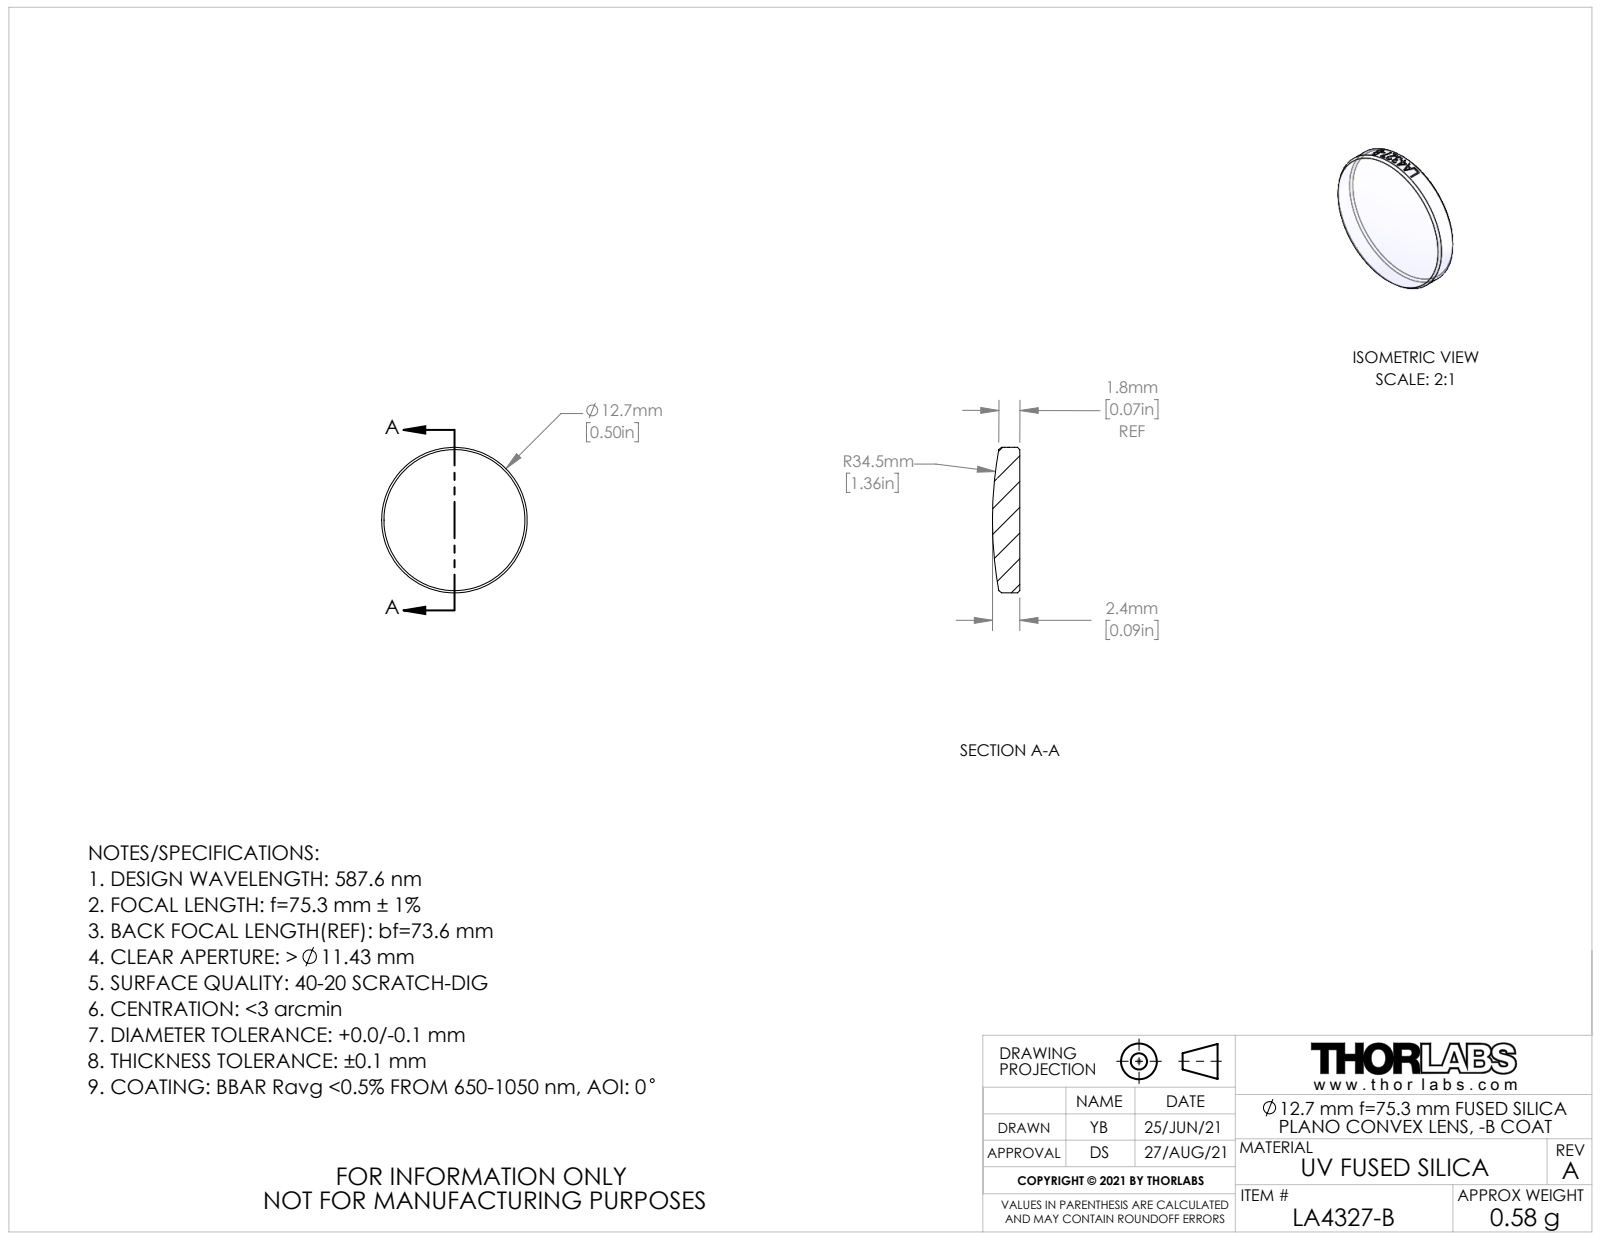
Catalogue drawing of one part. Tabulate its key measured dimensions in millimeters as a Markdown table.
| quantity | value |
| --- | --- |
| part name | CTN017897-E0W |
| STEP written by | SolidWorks 2018 (AUTOMOTIVE_DESIGN) |
| units | millimeters |
| bodies | 1 solid, 21 faces (1 planar, 14 cylindrical, 6 other) |
| overall size | 12.7 × 12.7 × 2.39 |
| volume | 264 mm³ |
| surface area | 318 mm² |
| round bosses / shafts (diameter × count) | 12.7 × 1 |
